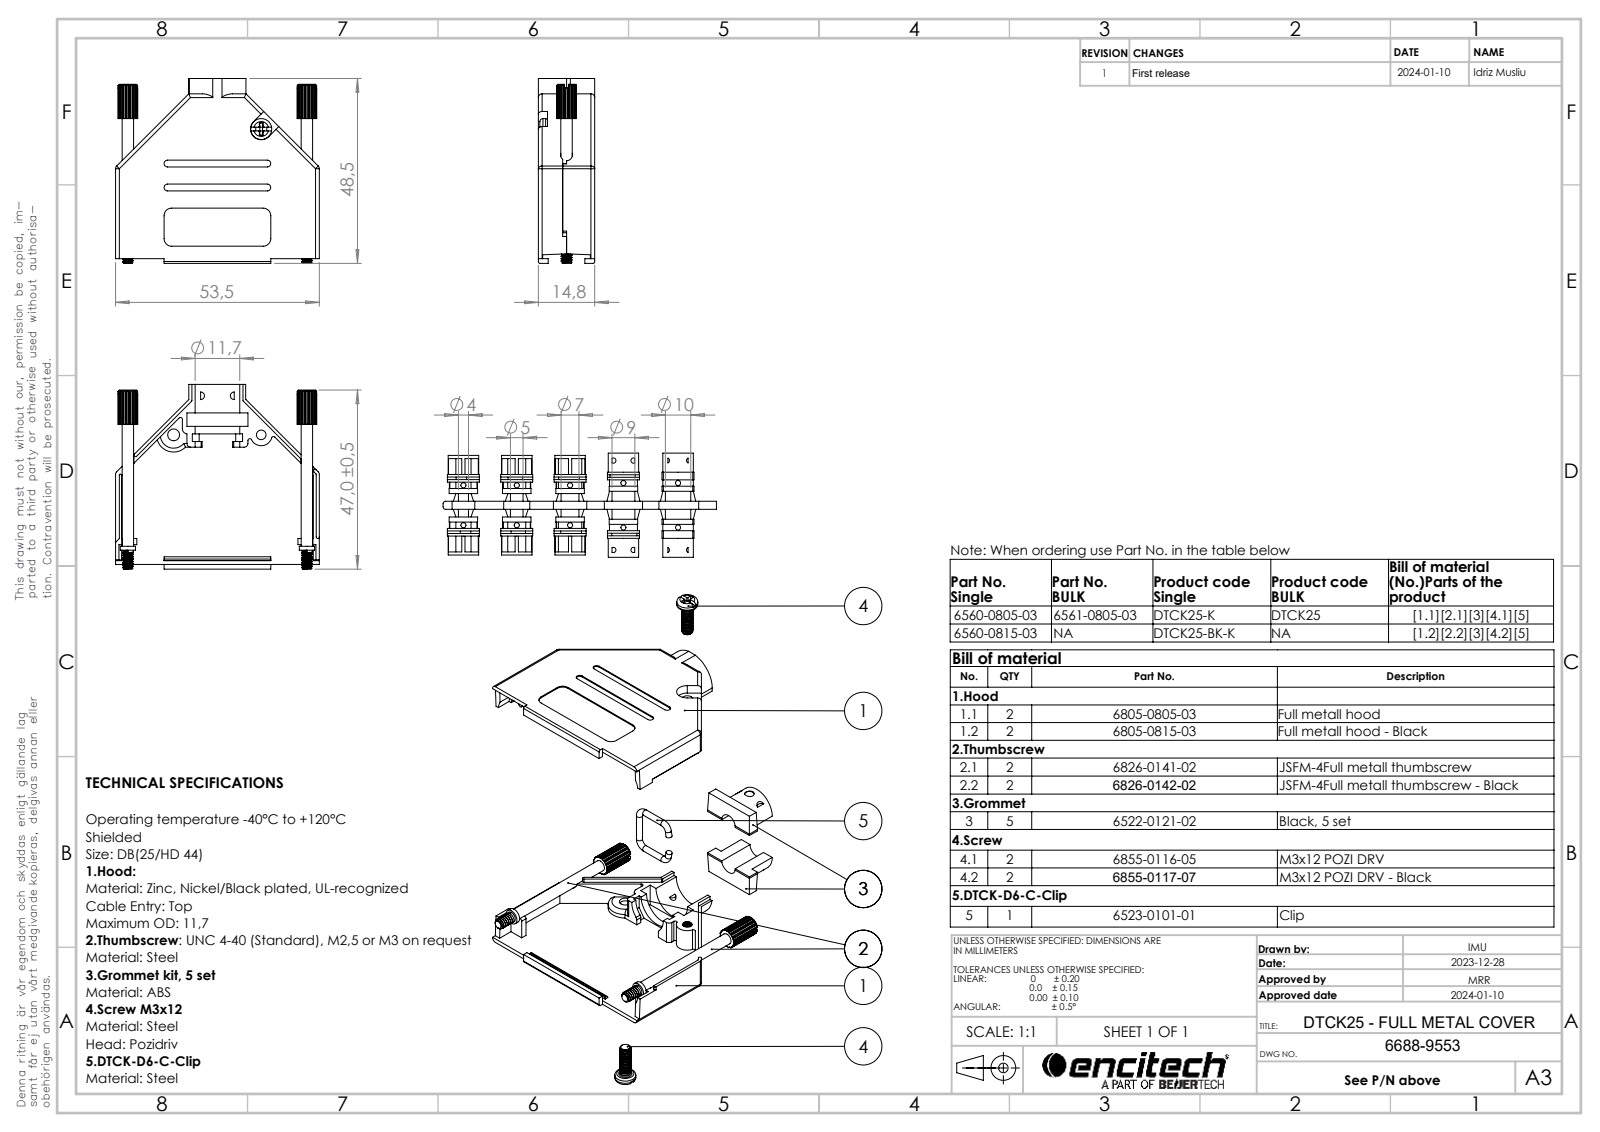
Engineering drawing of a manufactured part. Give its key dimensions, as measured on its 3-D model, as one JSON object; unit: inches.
{"part_name": "6805-0805-03; 6855-0116-05; 6688-9553; 6522-0121-02 (5mm) (+2 more)", "step_written_by": "SolidWorks 2021 (AUTOMOTIVE_DESIGN)", "units": "inches", "bodies": {"solids": 9, "faces": 766, "planar": 382, "cylindrical": 330, "other": 54}, "overall_size": [2.106, 1.909, 0.583], "volume_in3": 0.612, "surface_area_in2": 23.87, "round_holes": [[0.122, 4], [0.098, 3], [0.197, 1], [0.461, 1]], "round_bosses_or_shafts": [[0.063, 5], [0.118, 4], [0.217, 2], [0.157, 2], [0.11, 2], [0.591, 1], [0.453, 1]], "partial_cylinders_radius": [[0.039, 22], [0.01, 18], [0.02, 12], [0.016, 10], [0.035, 4], [0.079, 4], [0.197, 4], [0.014, 2]], "face_to_face_distances": [0.045, 0.537, 0.492, 0.583, 0.063, 0.291, 0.246, 0.033, 0.571, 0.28], "hole_center_spacings": [0.613, 0.925, 0.906, 1.85]}
